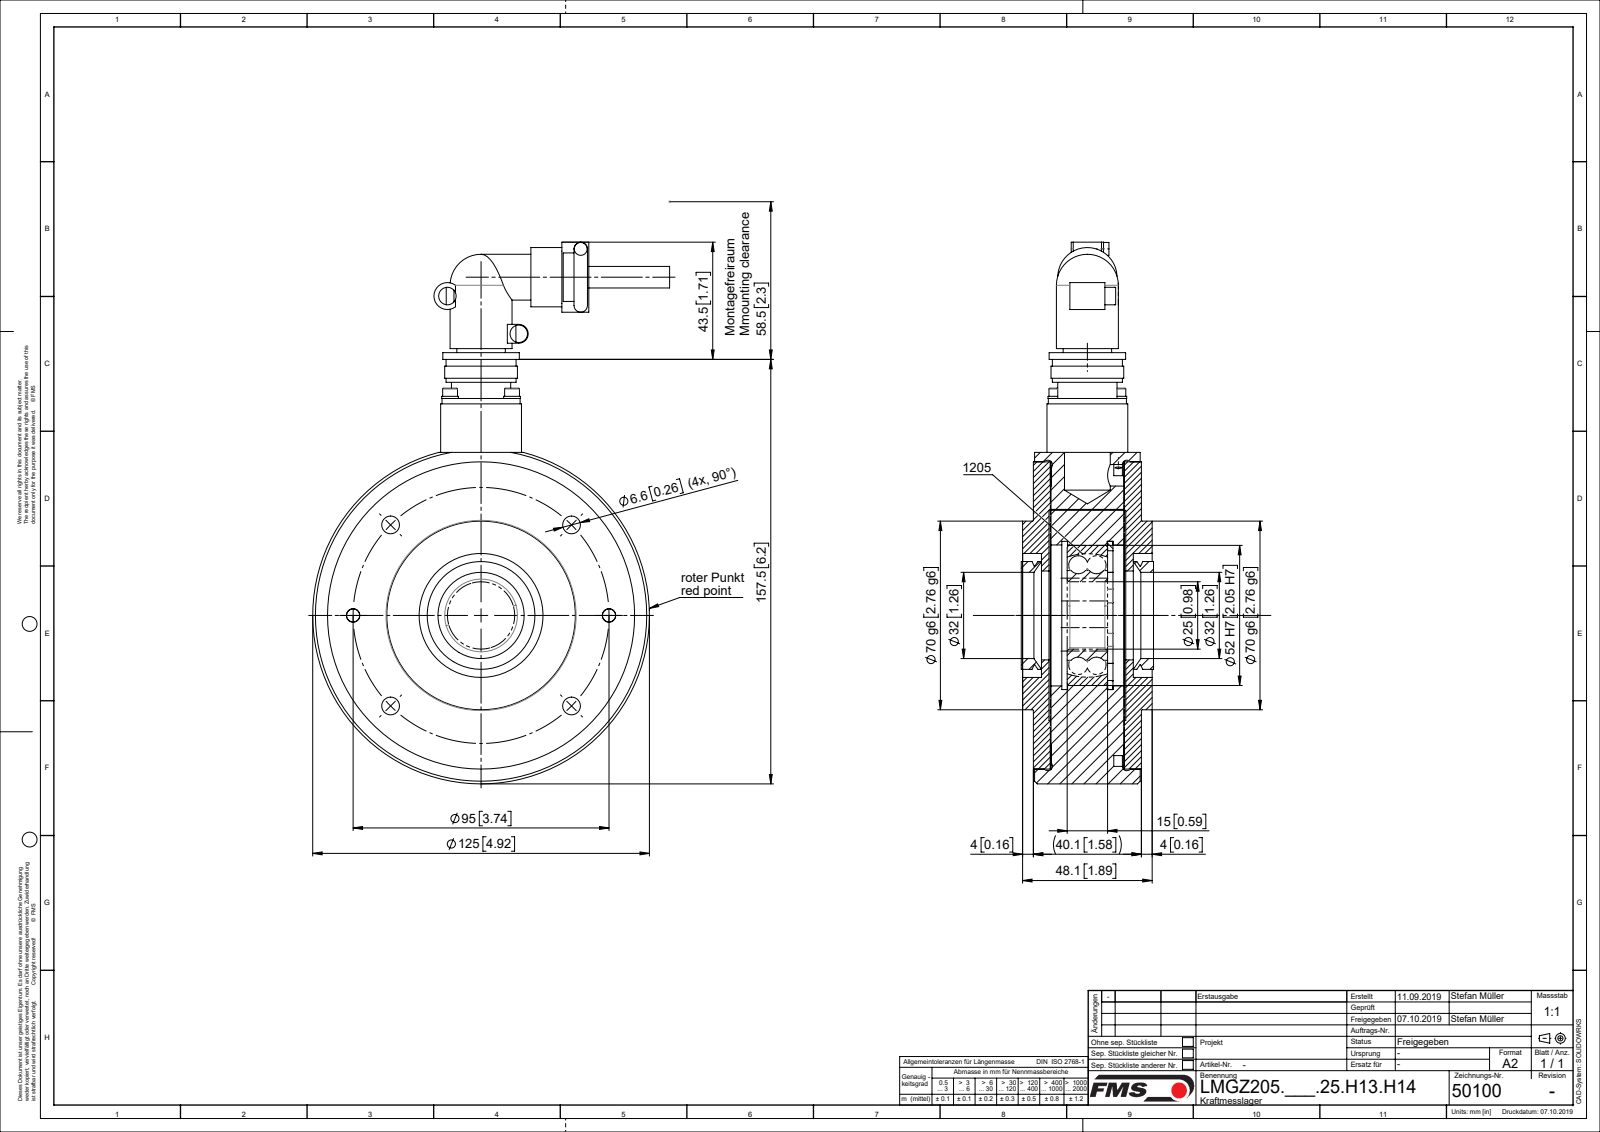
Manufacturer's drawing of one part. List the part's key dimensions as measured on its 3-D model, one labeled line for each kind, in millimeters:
Part name (STEP PRODUCT): L50100; L4817704; L49026; TEIL1 (+8 more)
STEP written by: Mechanical Desktop 2007 (CONFIG_CONTROL_DESIGN)
Units: millimetres
Bodies: 21 solids, 430 faces (121 planar, 250 cylindrical, 59 other)
Overall size (bounding box): 201 × 132.5 × 48.1
Volume: 492 816 mm³ · Surface area: 147 678 mm²
Round holes (diameter × count): ⌀6.6 ×8, ⌀2.6 ×4, ⌀3.2 ×4, ⌀3.4 ×4, ⌀3.5 ×4, ⌀5 ×2, ⌀11 ×2, ⌀23 ×1, ⌀25 ×1, ⌀31 ×1, ⌀33 ×1, ⌀37.9 ×1
Round bosses / shafts (diameter × count): ⌀6.2 ×4, ⌀5.5 ×4, ⌀3 ×4, ⌀22 ×2, ⌀10 ×2, ⌀6.5 ×2, ⌀6 ×2, ⌀4.8 ×2
Partial cylindrical surfaces — rounded edges, fillets, slot ends (radius × count): R5 ×17, R2.5 ×2, R3.5 ×1, R47 ×1
Main face-to-face distances: 27.25, 33.55, 6.3, 6.55, 33.8, 27, 27.5, 4, 10.55, 40.1
Hole centre spacings: 36.36, 47.5, 67.18, 87.77, 16.26, 23, 32.53, 95
